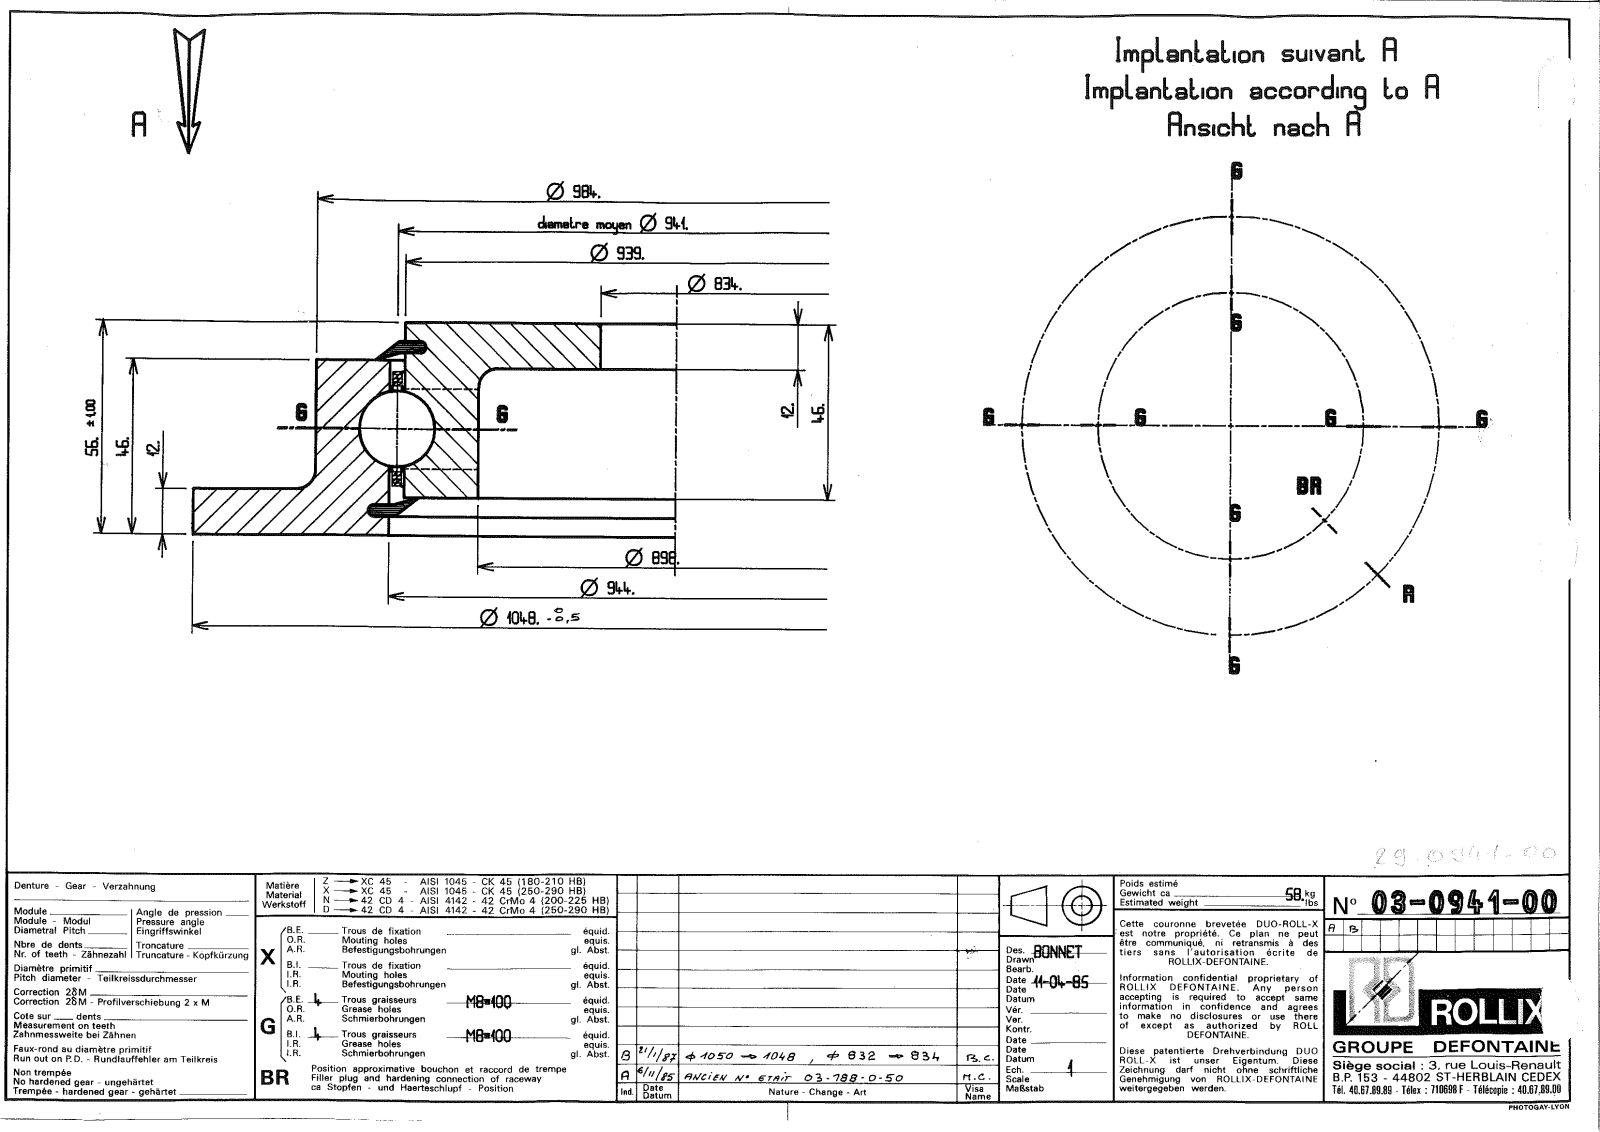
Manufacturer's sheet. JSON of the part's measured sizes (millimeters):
{"part_name": "23-0941-00", "step_written_by": "SolidWorks 2016 (CONFIG_CONTROL_DESIGN)", "units": "millimeters", "bodies": {"solids": 13, "faces": 258, "planar": 94, "cylindrical": 52, "other": 112}, "overall_size": [1048, 1048, 56], "volume_mm3": 7009000, "surface_area_mm2": 1414000, "round_holes": [[7, 8], [834, 1], [898, 1], [945.5, 1]], "round_bosses_or_shafts": [[8, 8], [1048, 1], [984, 1], [936.5, 1]], "face_to_face_distances": [12, 44, 56, 10, 46, 2, 34, 32, 36, 8.05], "hole_center_spacings": [0.4, 0.64]}
